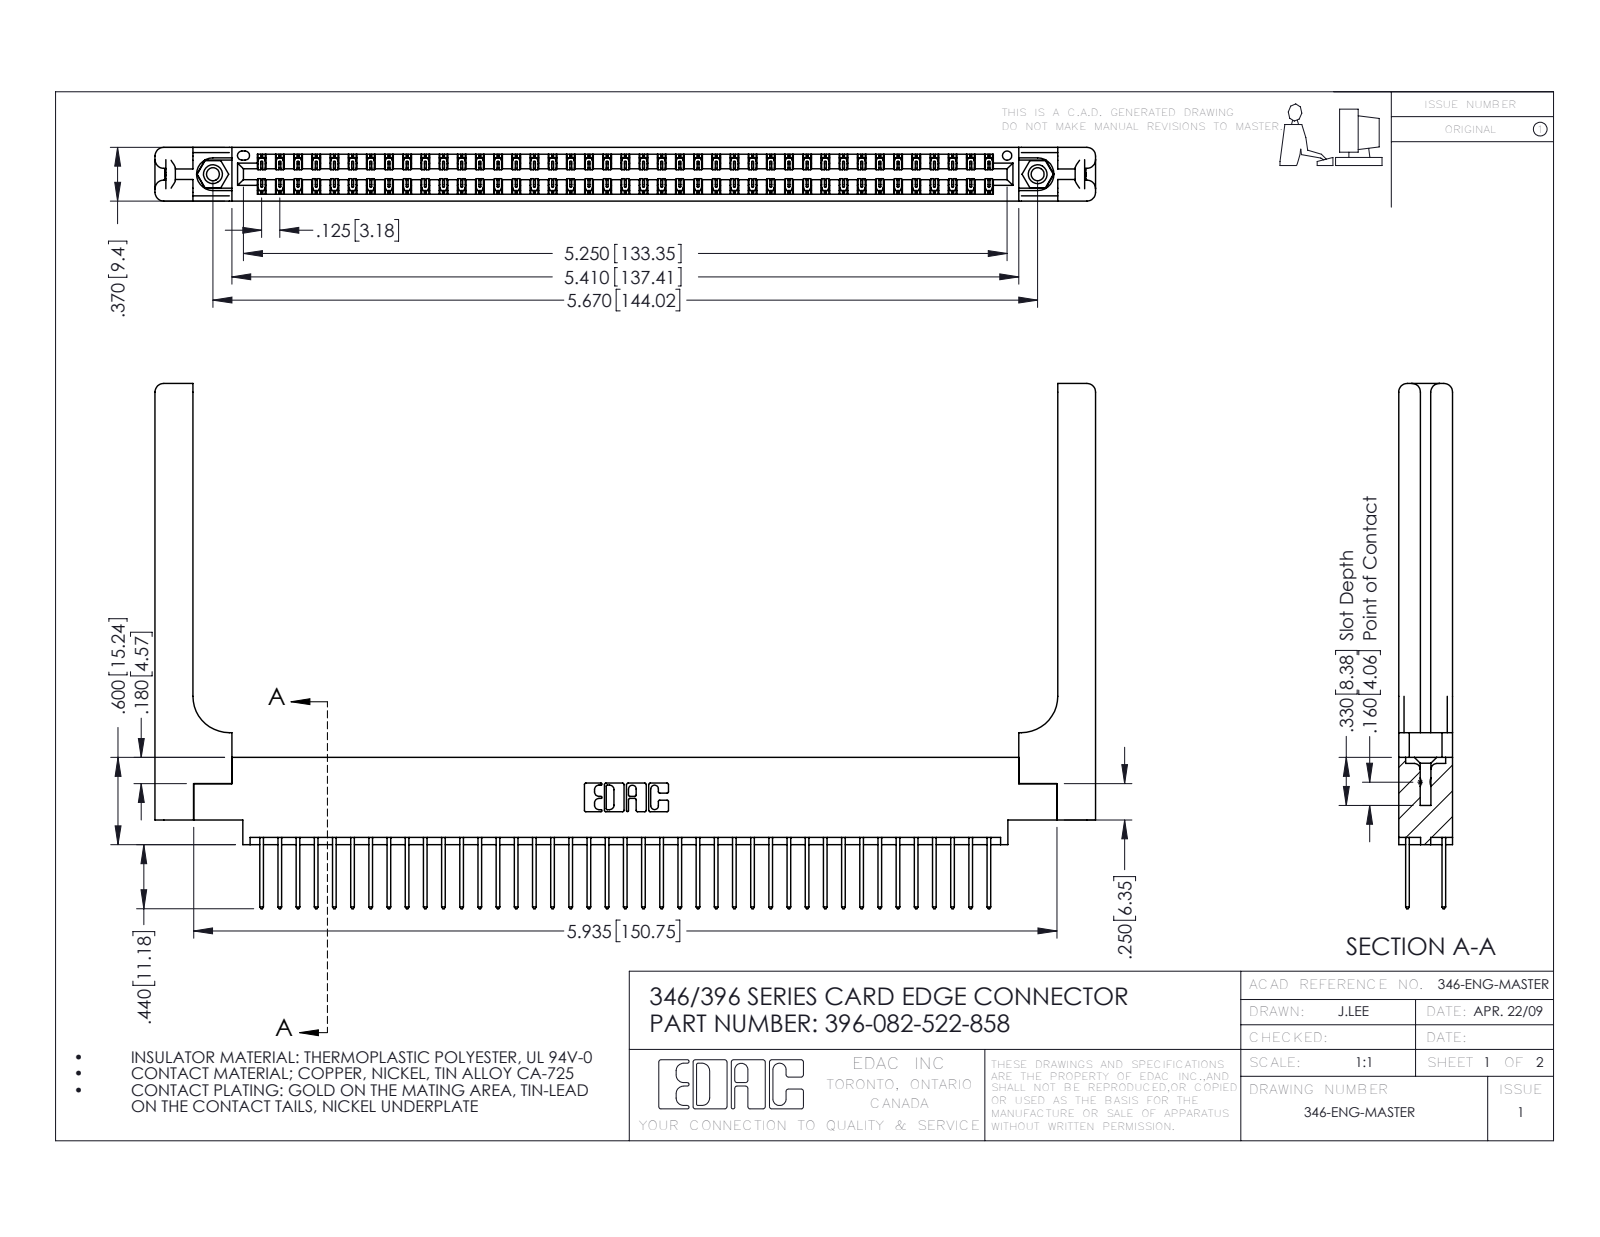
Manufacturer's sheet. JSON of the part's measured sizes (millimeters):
{"part_name": "396-082-522-858; 346 Part_0.170 Offset - 0.156 Dia-TH; 345-292-001_345-293-122; 345-250-001_345-250-001-102 (+1 more)", "step_written_by": "SolidWorks 2016 (CONFIG_CONTROL_DESIGN)", "units": "millimeters", "bodies": {"solids": 87, "faces": 4646, "planar": 3098, "cylindrical": 1488, "other": 60}, "overall_size": [164.2, 91.7, 9.4], "volume_mm3": 23560, "surface_area_mm2": 28190, "round_holes": [[2.3, 2], [3.2, 2], [4, 2], [1.6, 1]], "round_bosses_or_shafts": [[3.9, 2]], "partial_cylinders_radius": [[0.2, 123], [0.3, 82], [0.3, 22], [1.5, 16], [0.2, 6], [0.8, 6], [0.7, 3], [0.4, 2]], "face_to_face_distances": [1.2, 8.2, 9.4, 1.8, 6.4, 0.6, 7.6, 3.8, 3.8, 7], "hole_center_spacings": [6.2, 138.7, 144]}
